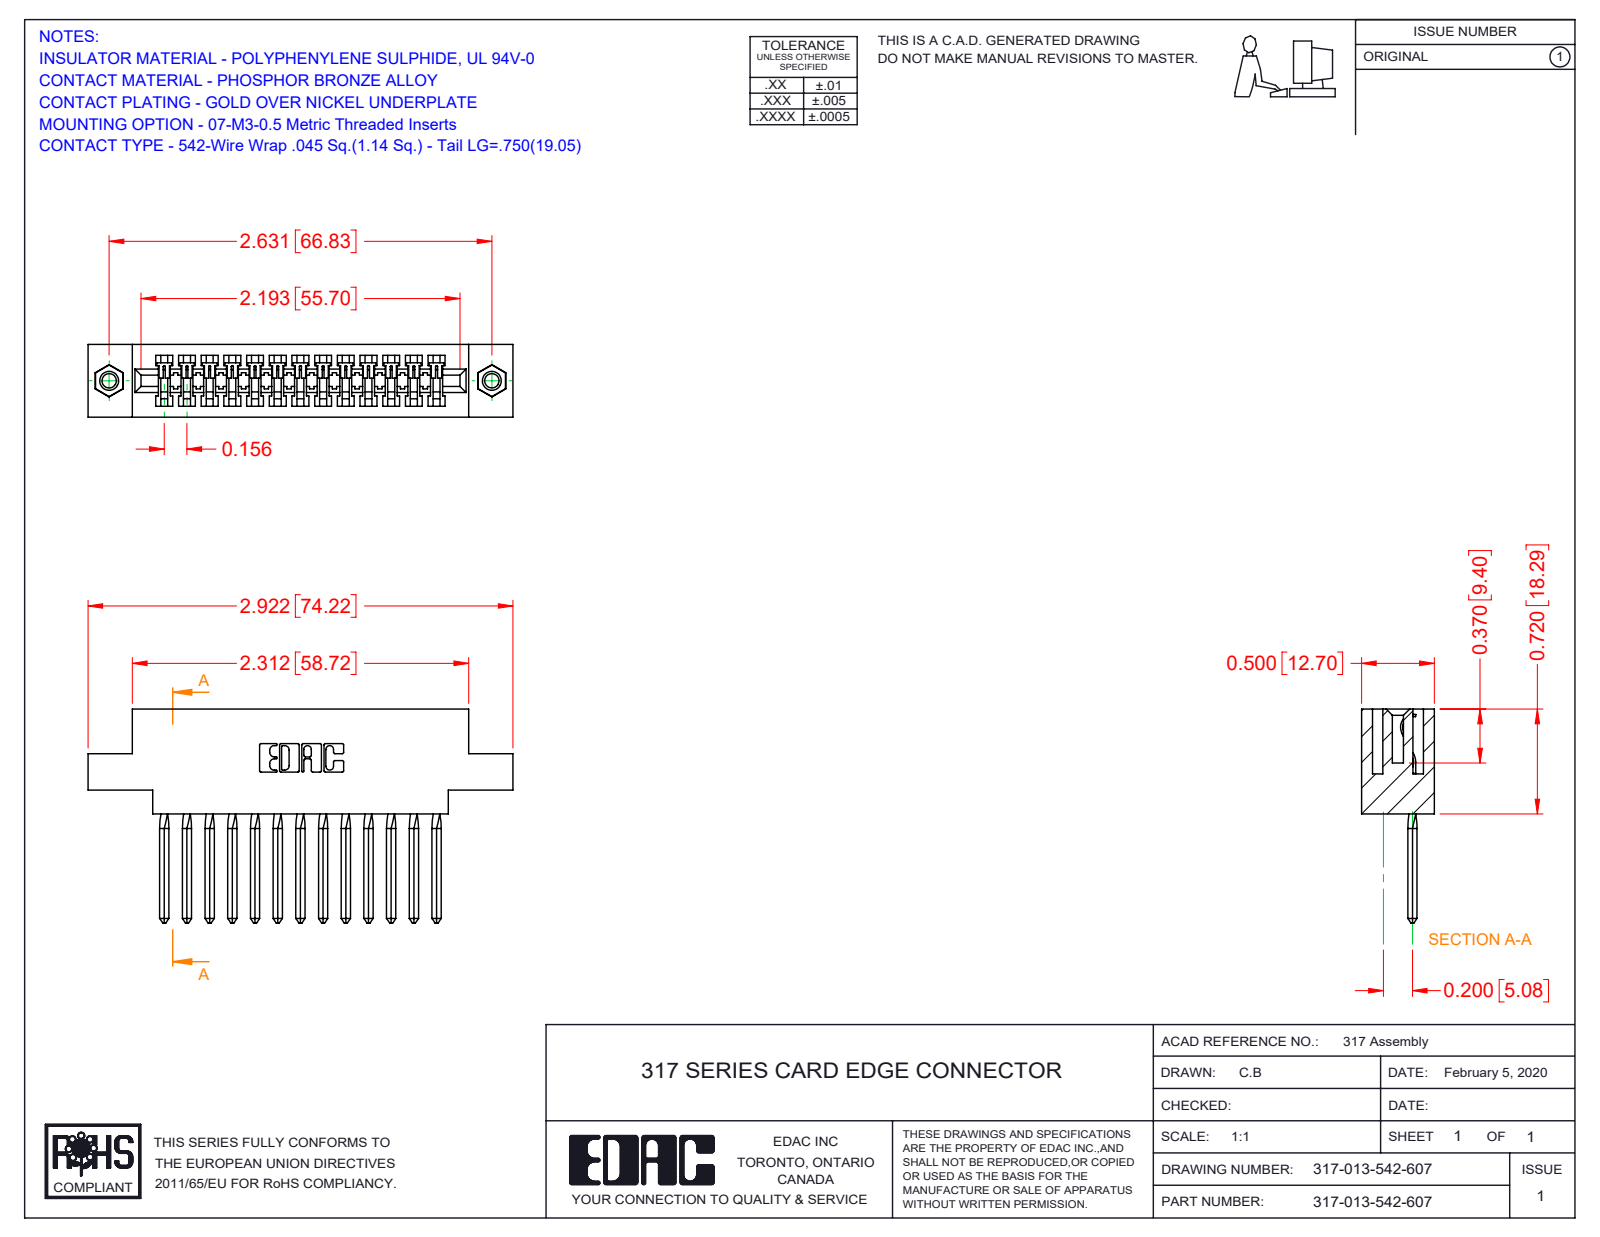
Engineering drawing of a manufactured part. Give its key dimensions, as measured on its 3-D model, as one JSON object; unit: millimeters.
{"part_name": "345-250-001_345-250-005-103; 317-013-542-607; 317-290-003_542; 317 Part_.156 Dia - TI", "step_written_by": "SolidWorks 2016 (CONFIG_CONTROL_DESIGN)", "units": "millimeters", "bodies": {"solids": 16, "faces": 1137, "planar": 922, "cylindrical": 147, "other": 68}, "overall_size": [74.2, 37.3, 12.7], "volume_mm3": 10700, "surface_area_mm2": 12410, "round_holes": [[2.5, 2], [3.2, 2], [4, 2]], "round_bosses_or_shafts": [[3.9, 2]], "partial_cylinders_radius": [[0.2, 26], [0.3, 22], [0.2, 6], [0.8, 6], [0.7, 3], [1.9, 1], [2.3, 1], [2.5, 1]], "face_to_face_distances": [12.7, 1.9, 10.8, 2.8, 1.7, 8.9, 5.6, 3.5, 18.3, 8.4], "hole_center_spacings": [66.8]}
